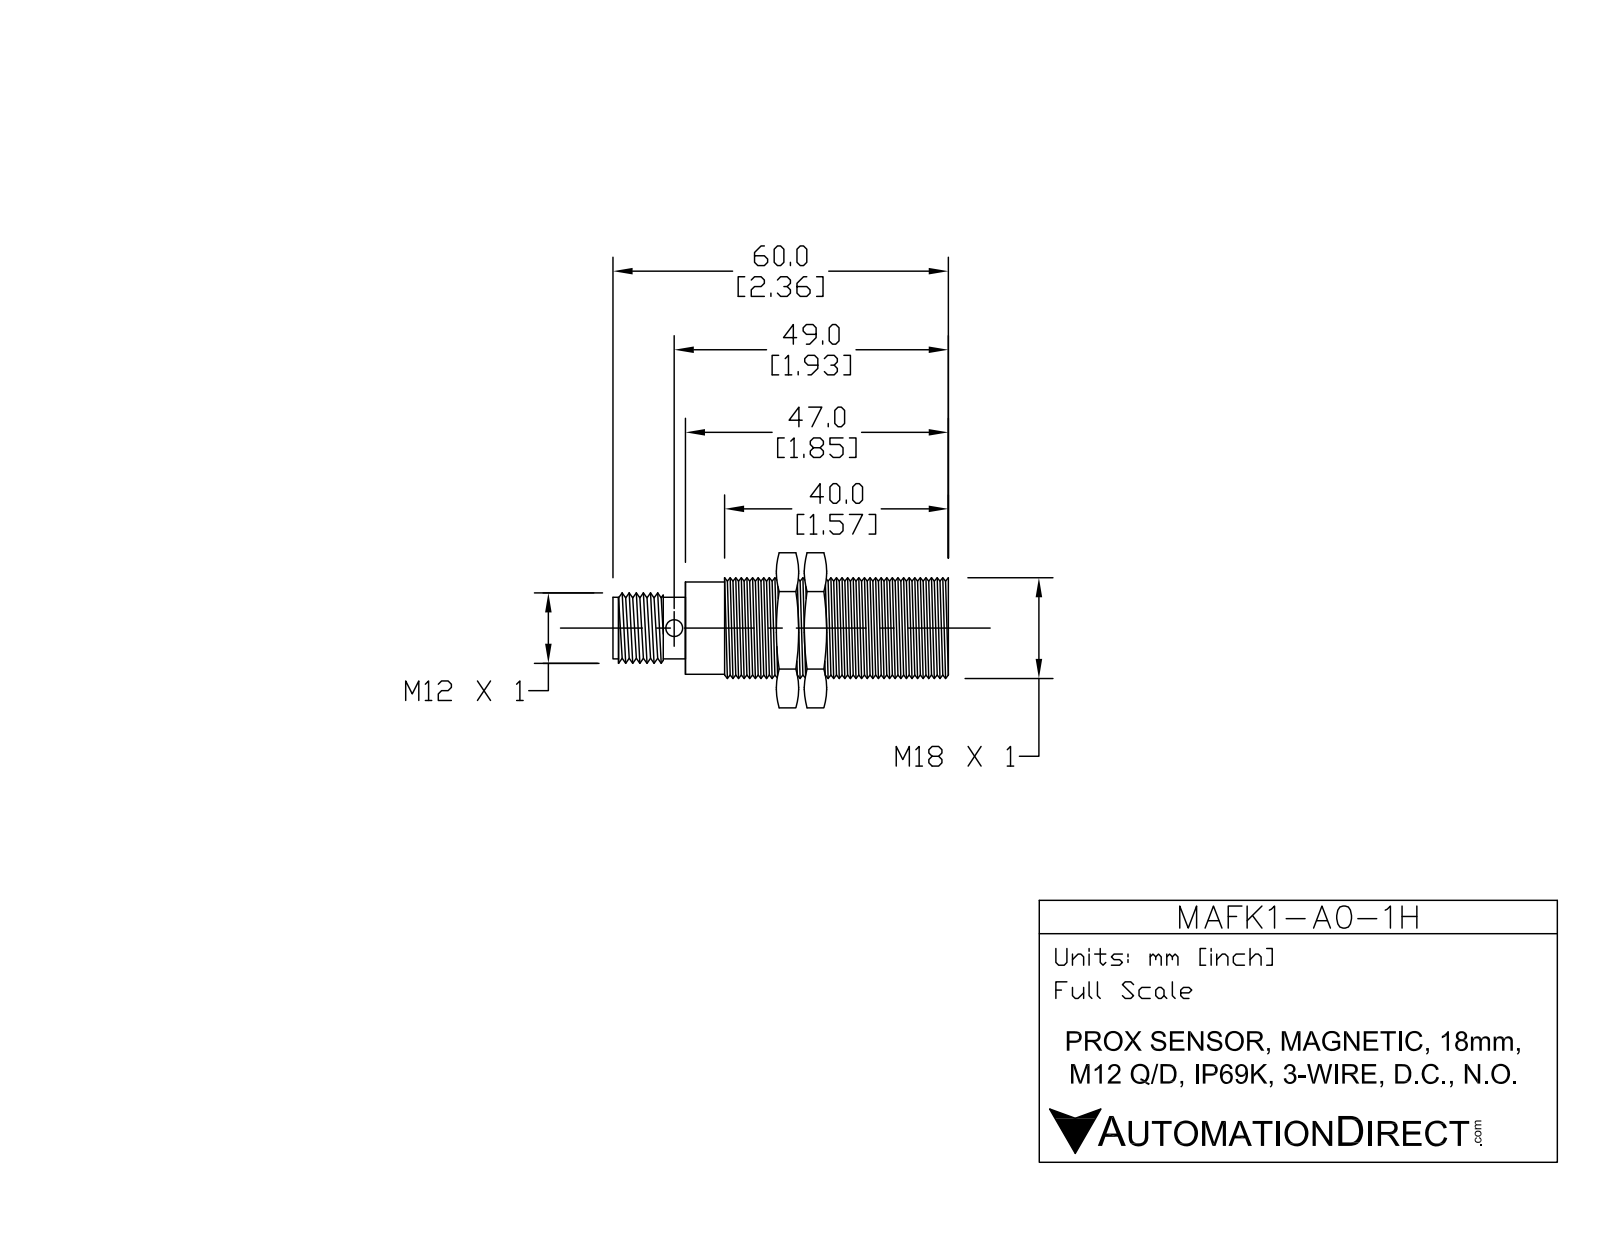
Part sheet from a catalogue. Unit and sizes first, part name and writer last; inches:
Units: inches
Overall size (bounding box): 2.362 × 1.091 × 0.945
Round holes (diameter × count): ⌀0.118 ×2, ⌀0.331 ×1, ⌀0.666 ×1
Round bosses / shafts (diameter × count): ⌀0.709 ×1, ⌀0.654 ×1, ⌀0.63 ×1, ⌀0.472 ×1, ⌀0.445 ×1, ⌀0.417 ×1
Partial cylindrical surfaces — rounded edges, fillets, slot ends (radius × count): R0.024 ×1, R0.203 ×1
Main face-to-face distances: 0.157, 0.945, 0.591, 0.315, 0.433, 0.748, 1.26, 1.417, 1.102, 1.85
Volume: 0.892 in³ · Surface area: 9.191 in²
Bodies: 3 solids, 109 faces (28 planar, 34 cylindrical, 47 other)
Part name (STEP PRODUCT): MAFK1-A0-1H
STEP written by: SolidWorks 2017 (AUTOMOTIVE_DESIGN)
